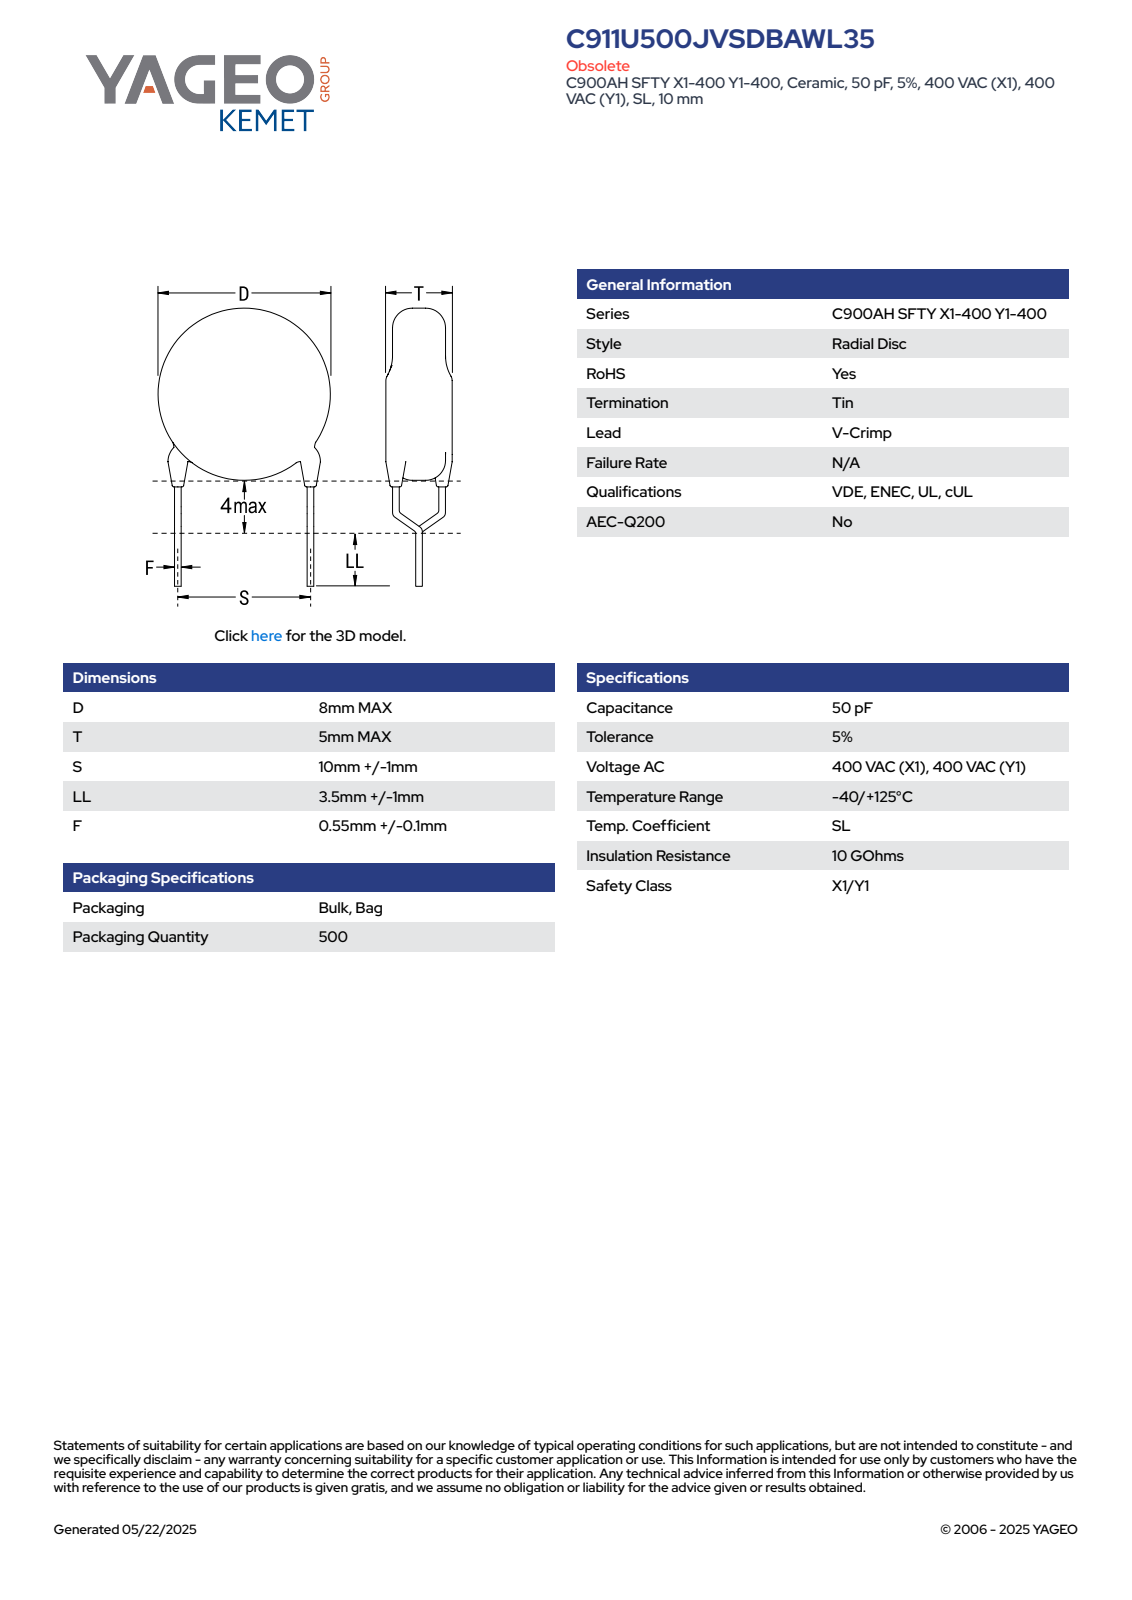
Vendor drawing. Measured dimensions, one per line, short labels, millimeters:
name: CCD_VCC900_D8T5S10LL4.5F0.65
written by: SolidWorks 2014 (AUTOMOTIVE_DESIGN)
unit: mm
bodies: 5 solids, 93 faces (65 planar, 16 cylindrical, 12 other)
size: 16.3 × 10.65 × 5
volume: 252 mm³; area: 262 mm²
bosses: 6× ⌀0.65, 1× ⌀8
face distances: 5, 7.4, 1.04, 12.82, 5.42, 11.78, 4.38, 0.84, 0.45, 0.39
